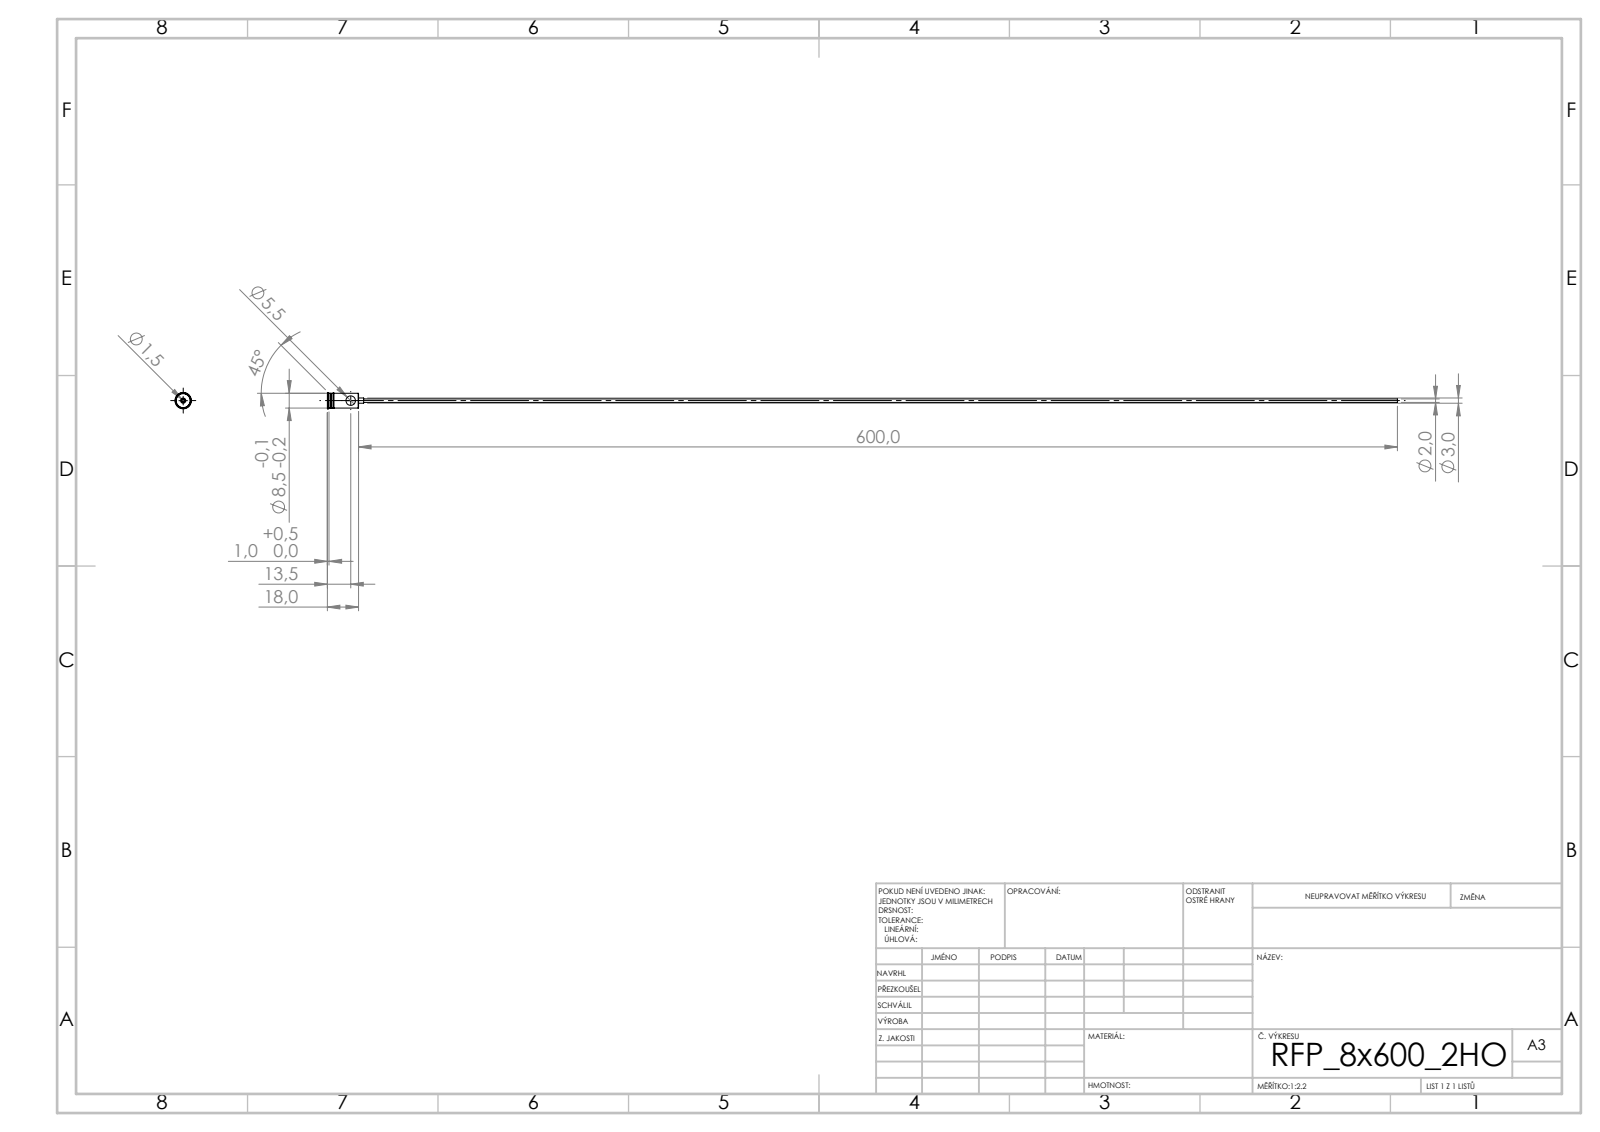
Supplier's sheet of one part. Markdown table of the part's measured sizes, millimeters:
| quantity | value |
| --- | --- |
| STEP written by | SolidWorks 2019 (CONFIG_CONTROL_DESIGN) |
| units | millimeters |
| bodies | 1 solid, 44 faces (20 planar, 16 cylindrical, 8 other) |
| overall size | 618 × 9.5 × 9.5 |
| volume | 1 650 mm³ |
| surface area | 7 352 mm² |
| round holes (diameter × count) | 1.5 × 1, 5.5 × 1 |
| round bosses / shafts (diameter × count) | 9.5 × 1, 8.5 × 1, 3 × 1, 2 × 1 |
| main face-to-face distances | 18, 16, 2, 3.9, 15.7, 2.3, 3, 18.7, 19, 21 |
